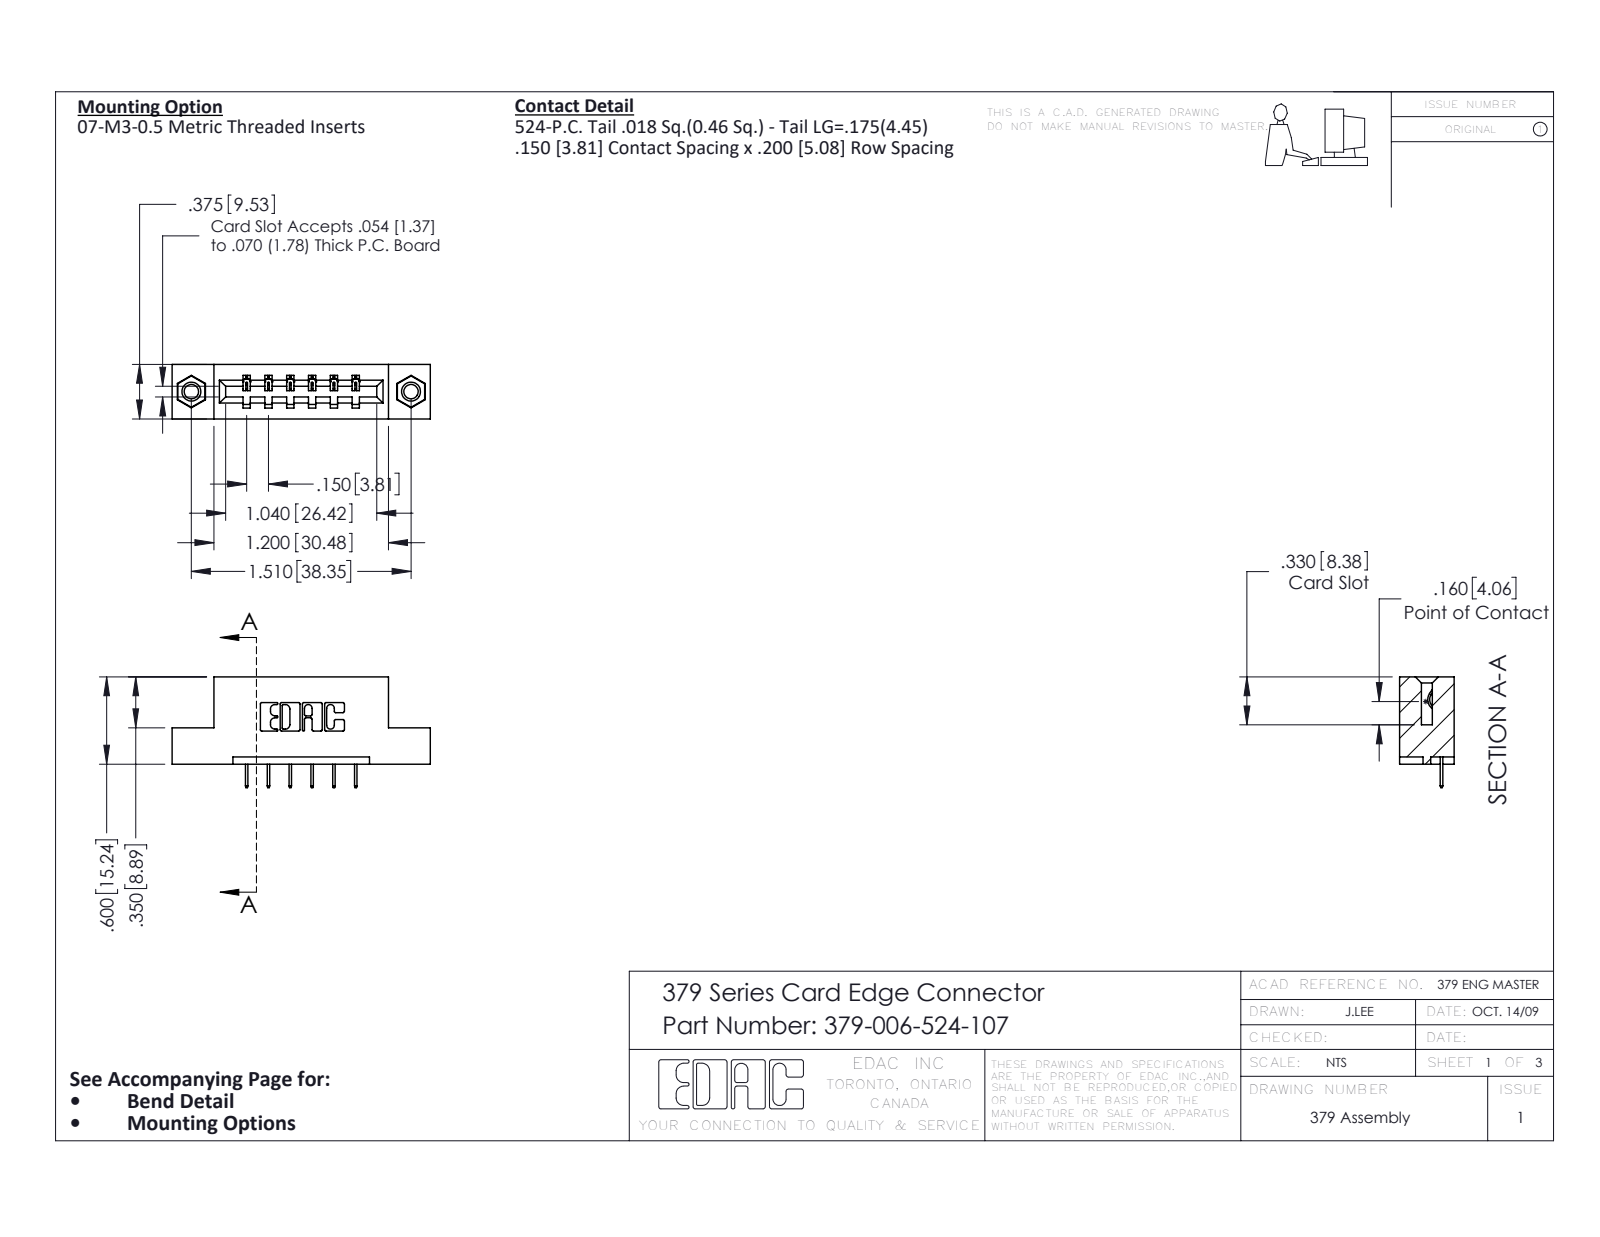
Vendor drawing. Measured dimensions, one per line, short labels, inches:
name: 345-292-001_345-293-124; 379 Part_Flush - .156 Dia - TI; 379-006-524-107; 345-250-001_345-250-005-103
written by: SolidWorks 2016 (CONFIG_CONTROL_DESIGN)
unit: in
bodies: 9 solids, 546 faces (390 planar, 140 cylindrical, 16 other)
size: 1.775 × 0.762 × 0.375
volume: 0.261 in³; area: 6.429 in²
holes: 2× ⌀0.098, 2× ⌀0.125, 2× ⌀0.156
bosses: 2× ⌀0.155
rounds: 22× R0.01, 12× R0.006, 6× R0.007, 6× R0.031, 3× R0.026, 1× R0.014, 1× R0.022, 1× R0.024
face distances: 0.3, 0.2, 0.375, 0.05, 0.15, 0.075, 0.25, 0.35, 0.6, 0.55
hole spacings: 1.51
